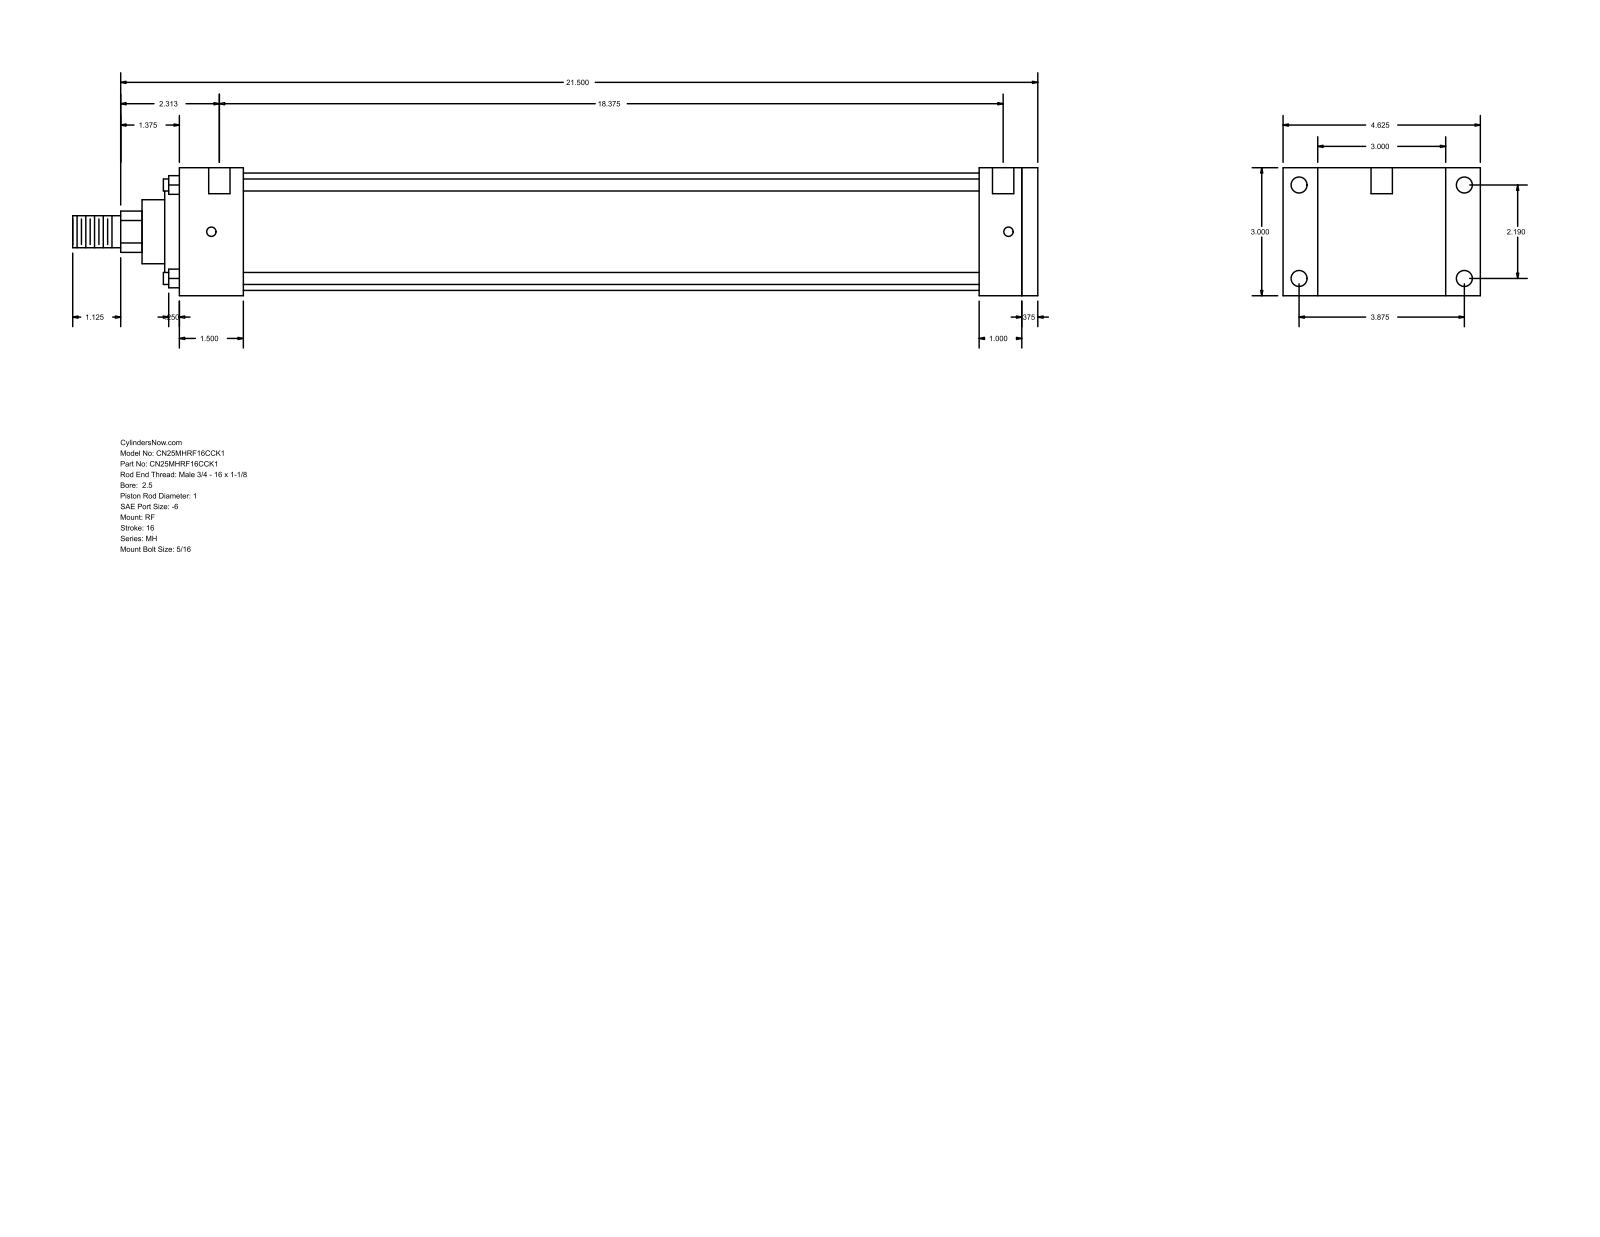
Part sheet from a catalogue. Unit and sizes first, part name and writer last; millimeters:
Units: millimetres
Overall size (bounding box): 574.67 × 117.47 × 76.2
Round holes (diameter × count): ⌀5.56 ×4, ⌀9.53 ×4, ⌀12.7 ×2
Round bosses / shafts (diameter × count): ⌀7.14 ×4, ⌀69.85 ×1, ⌀60.33 ×1, ⌀38.1 ×1, ⌀25.4 ×1, ⌀19.05 ×1
Partial cylindrical surfaces — rounded edges, fillets, slot ends (radius × count): R12.29 ×1
Main face-to-face distances: 76.2, 9.52, 511.18, 501.66, 25.4, 34.92, 476.26, 38.11, 438.15, 463.55
Hole centre spacings: 55.62, 98.42, 113.05, 474.66, 3.18, 4.76, 466.72, 469.9
Bodies: 0 solids, 94 faces (65 planar, 29 cylindrical, 0 other)
Part name (STEP PRODUCT): MH_RF__0250_1
STEP written by: GSSL Pune (CONFIG_CONTROL_DESIGN)
